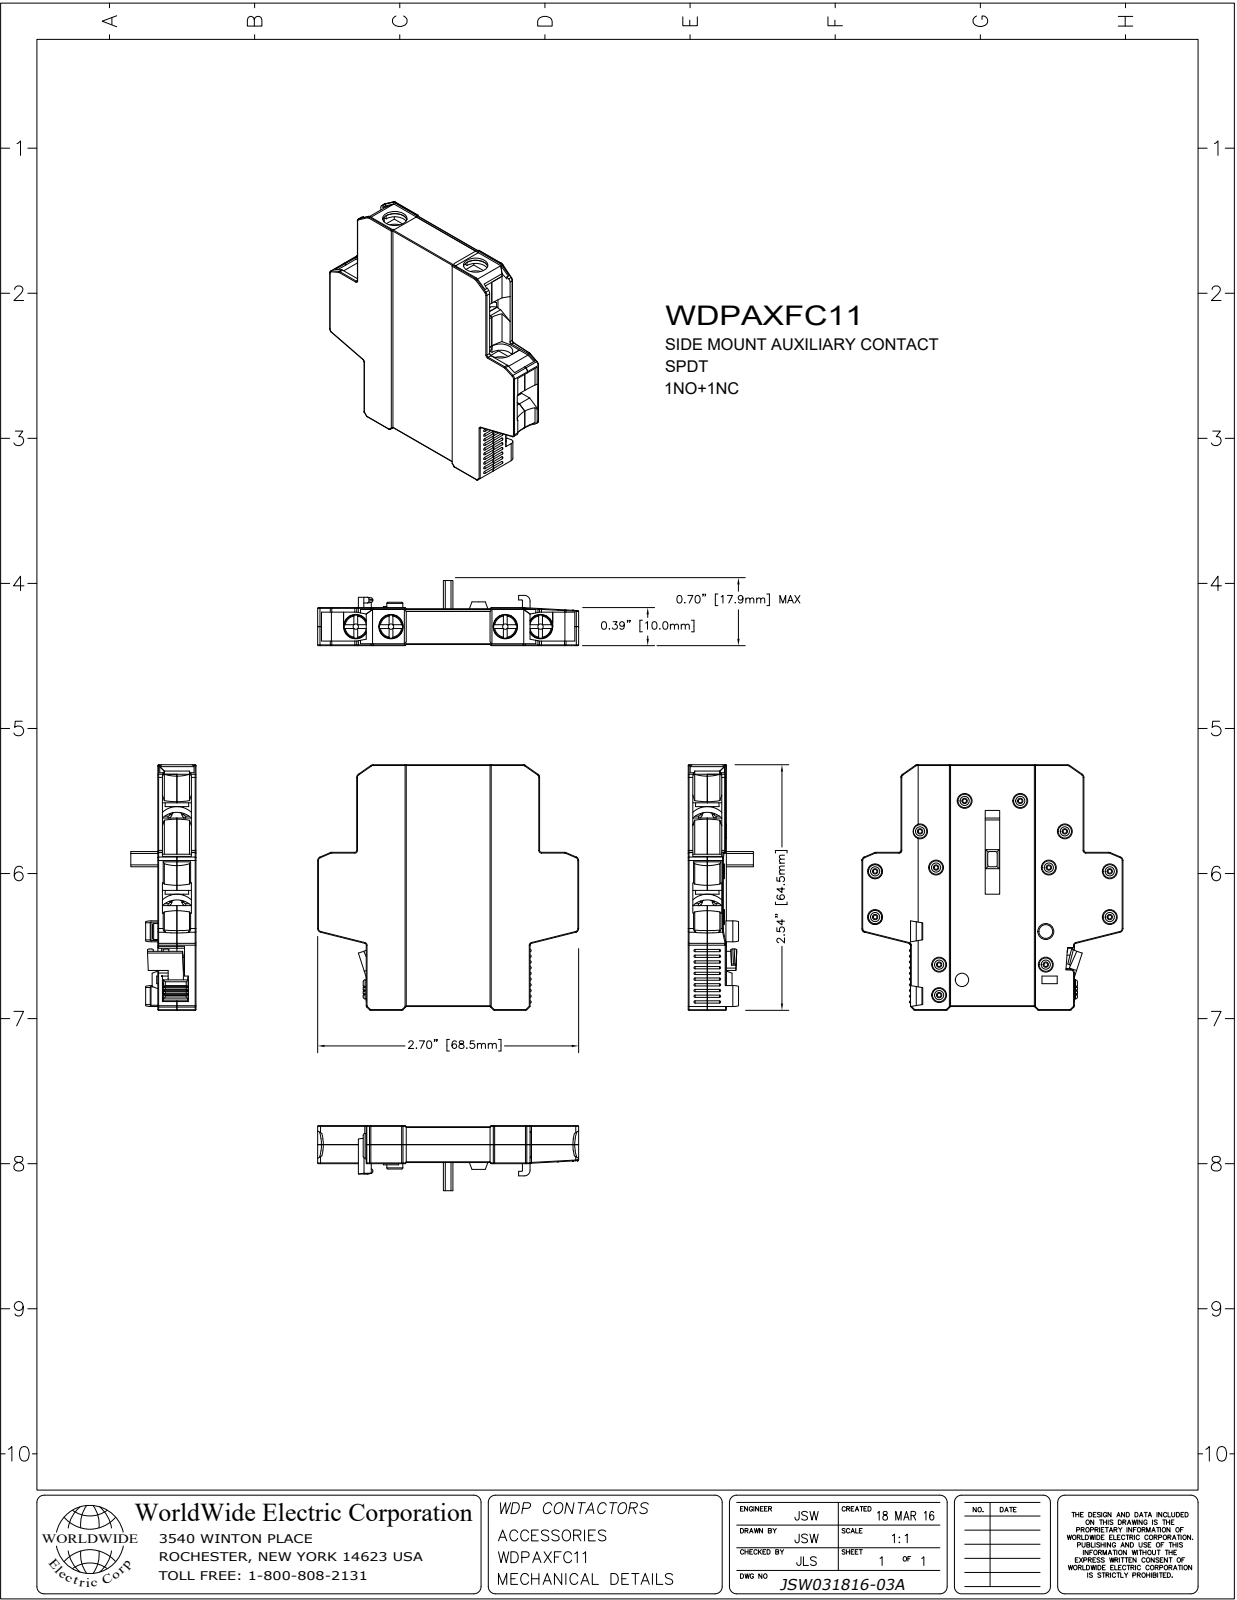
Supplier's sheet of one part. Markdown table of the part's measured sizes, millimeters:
| quantity | value |
| --- | --- |
| part name | WDPAXFC11 |
| STEP written by | SolidWorks 2017 (AUTOMOTIVE_DESIGN) |
| units | millimeters |
| bodies | 2 solids, 924 faces (738 planar, 166 cylindrical, 20 other) |
| overall size | 69.3 × 66.8 × 22.2 |
| volume | 12 600 mm³ |
| surface area | 15 520 mm² |
| round holes (diameter × count) | 1.5 × 2, 2.5 × 2, 3.1 × 2 |
| round bosses / shafts (diameter × count) | 6 × 4, 2.5 × 2 |
| partial cylindrical surfaces (radius × count) | 0.3 × 107, 3 × 6, 1.5 × 5, 0.5 × 4, 0.8 × 2, 0.8 × 2, 1 × 2, 2 × 2 |
| main face-to-face distances | 1.2, 1.5, 2, 33.5, 2.5, 8.2, 6, 3.2, 10.2, 10.1 |
| hole center spacings | 24.5, 41.4, 29.4, 38 |
